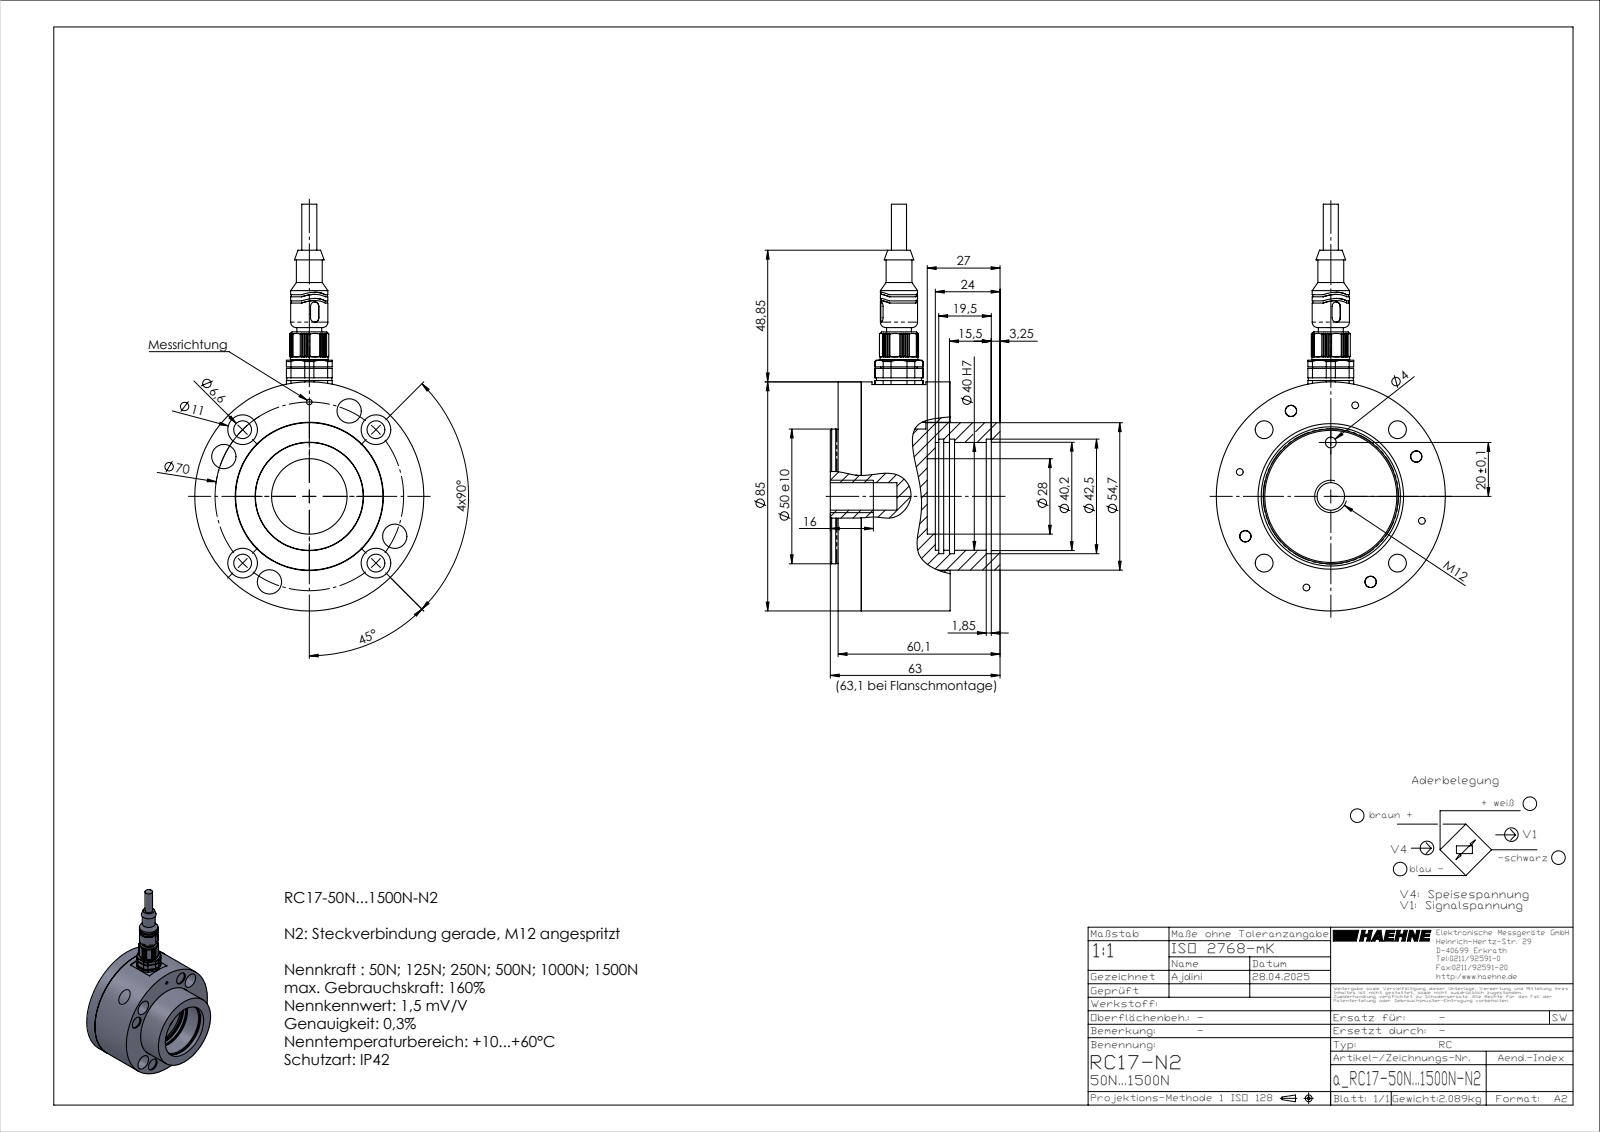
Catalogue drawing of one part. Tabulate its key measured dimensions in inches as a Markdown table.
| quantity | value |
| --- | --- |
| part name | a_RC-N2 Flanschmontage Scheibe; a_RC17-50N...1500N-N2; a_RC17-50N...1500N-N2 STEP |
| STEP written by | SolidWorks 2023 (AUTOMOTIVE_DESIGN) |
| units | inches |
| bodies | 14 solids, 901 faces (506 planar, 252 cylindrical, 143 other) |
| overall size | 5.942 × 3.346 × 2.484 |
| volume | 15.27 in³ |
| surface area | 120.4 in² |
| round holes (diameter × count) | 0.433 × 5, 0.043 × 4, 0.045 × 4, 0.063 × 4, 0.073 × 4, 0.098 × 4, 0.134 × 4, 0.165 × 4, 0.209 × 4, 0.26 × 4, 0.354 × 4, 0.047 × 1 |
| round bosses / shafts (diameter × count) | 0.335 × 4, 0.224 × 4, 0.197 × 4, 0.118 × 4, 0.071 × 4, 0.061 × 4, 0.059 × 4, 0.039 × 4 |
| partial cylindrical surfaces (radius × count) | 0.008 × 16, 0.012 × 10, 0.016 × 4, 0.021 × 4, 0.039 × 4, 0.05 × 4, 0.472 × 4, 0.063 × 2 |
| main face-to-face distances | 0.339, 0.118, 0.457, 1.299, 1.756, 1.638, 0.453, 0.114, 1.752, 0.079 |
| hole center spacings | 1.378, 1.949, 0.098, 0.139, 0.479, 0.713, 0.943, 1.165 |
